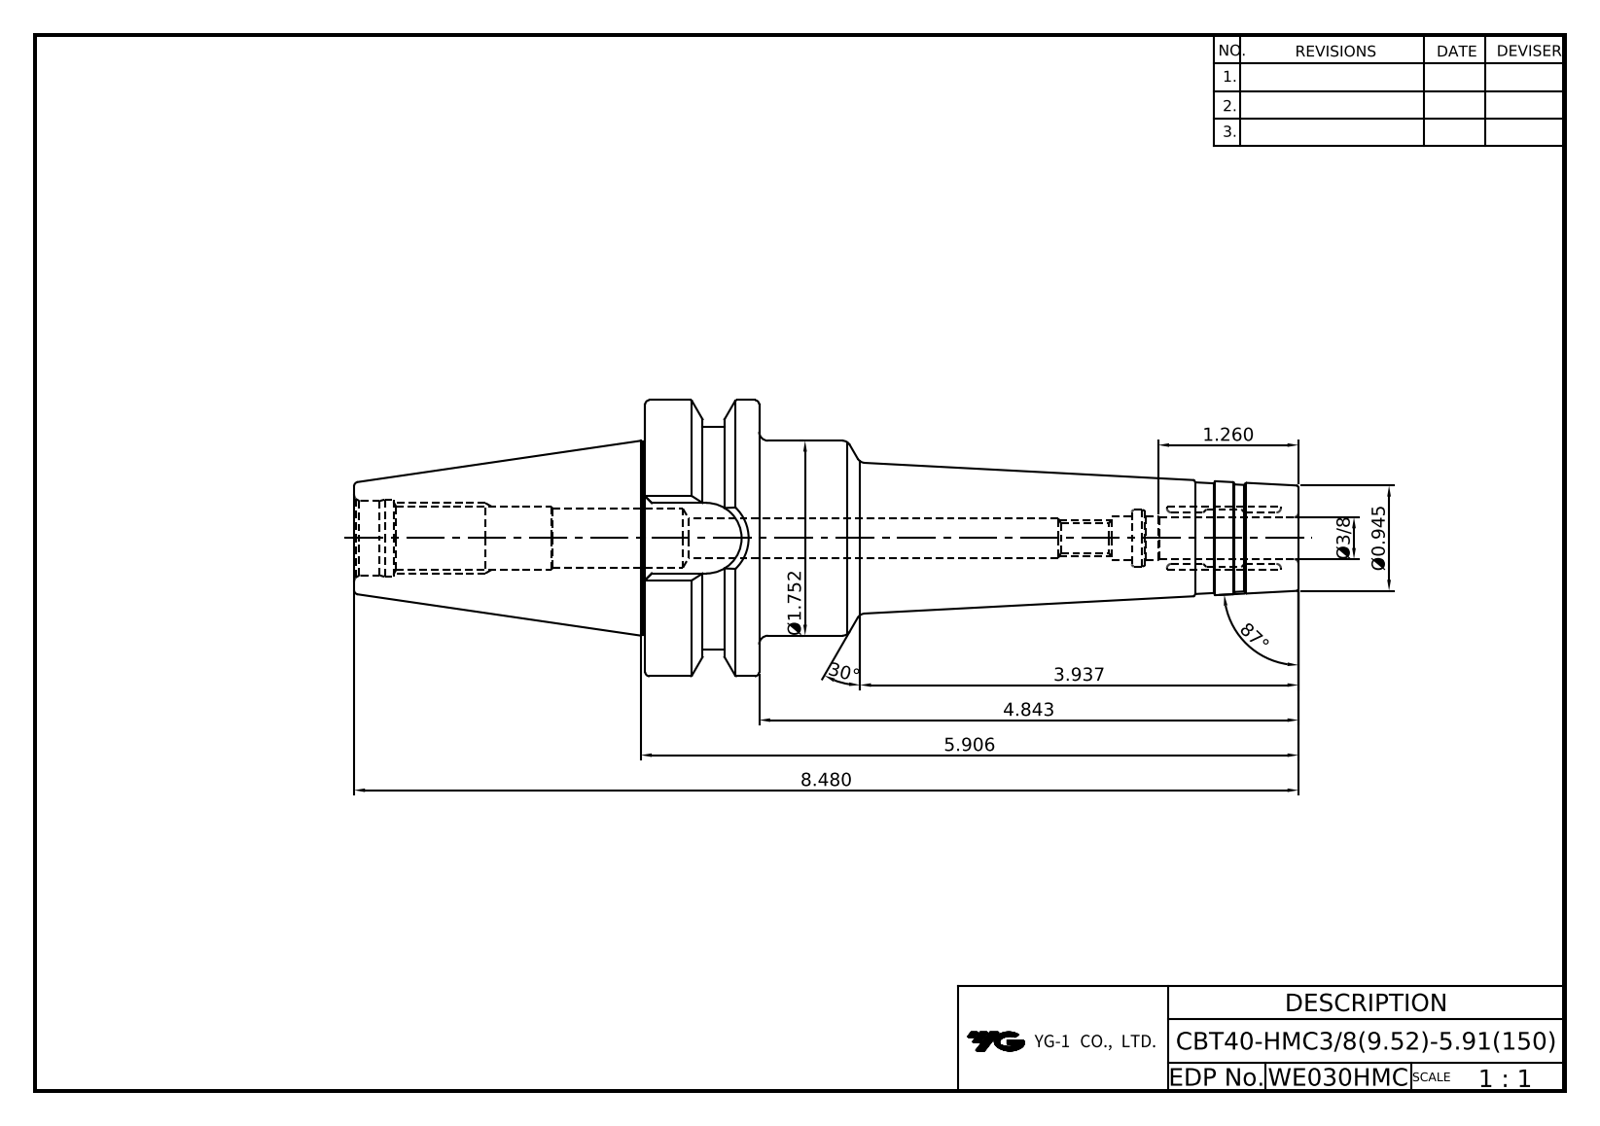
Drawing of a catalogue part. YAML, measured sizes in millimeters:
part_name: "LO-CBT40-HMC9.35-150"
step_written_by: "Autodesk Inventor 2022 (AUTOMOTIVE_DESIGN)"
units: millimeters
bodies: {solids: 1, faces: 83, planar: 24, cylindrical: 17, other: 42}
overall_size: [215.4, 63, 63]
volume: 216468
surface_area: 37536
round_holes:
  - {diameter: 6.92, count: 1}
  - {diameter: 9, count: 1}
  - {diameter: 9.35, count: 1}
  - {diameter: 9.95, count: 1}
  - {diameter: 13.5, count: 1}
  - {diameter: 13.84, count: 1}
  - {diameter: 17, count: 1}
  - {diameter: 17.6, count: 1}
round_bosses_or_shafts:
  - {diameter: 63, count: 1}
  - {diameter: 51, count: 1}
  - {diameter: 44.5, count: 1}
  - {diameter: 44, count: 1}
partial_cylinders:
  - {radius: 8.05, count: 1}
face_to_face_distances: [26, 149, 123, 45.2, 18.1, 7.9, 130.9, 13.1, 5, 12.9]
